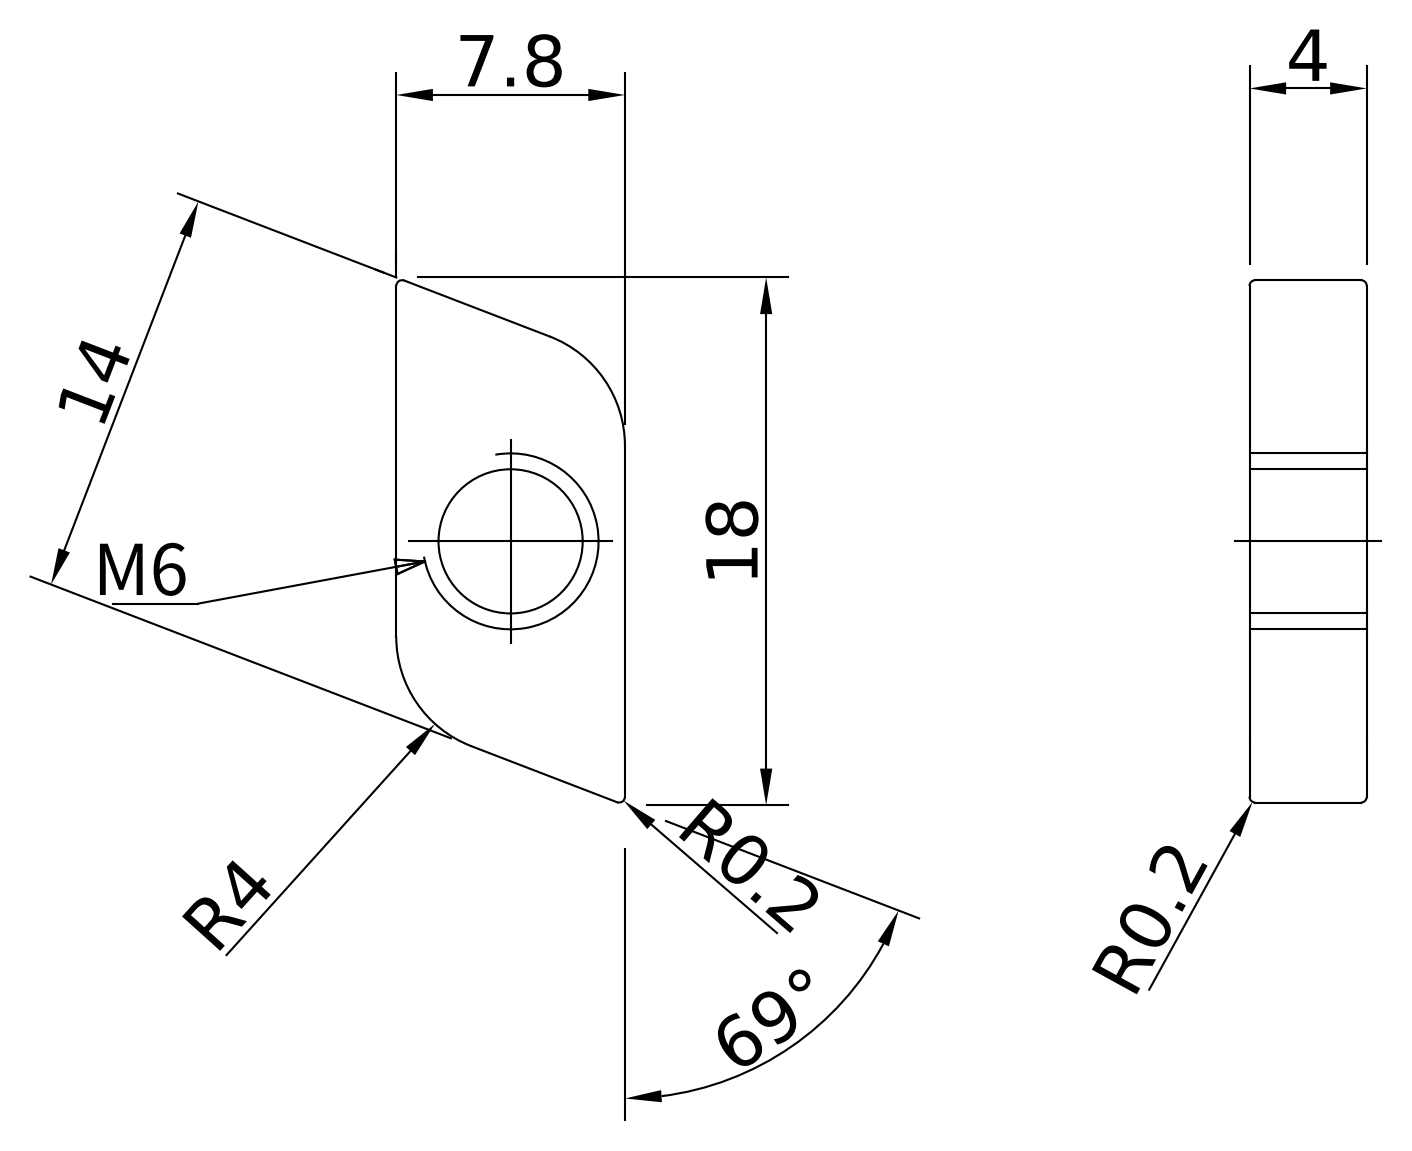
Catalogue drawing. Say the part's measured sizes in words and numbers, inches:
The part is named "CDDCU0000025". Its 3-D file was written by "Autodesk Inventor 2022 (AUTOMOTIVE_DESIGN)". It is 1 solid with 27 faces: 6 planar, 13 cylindrical and 8 other. Overall it measures 0.702 by 0.307 by 0.157 inches. Its volume is 0.023 cubic inches and its surface area 0.657 square inches. Round holes: 1 of diameter 0.194. Partial cylindrical surfaces (rounded edges, fillets, slot ends): 10 of radius 0.008, 2 of radius 0.157. The main face-to-face distances are 0.157, 0.307, 0.551.
